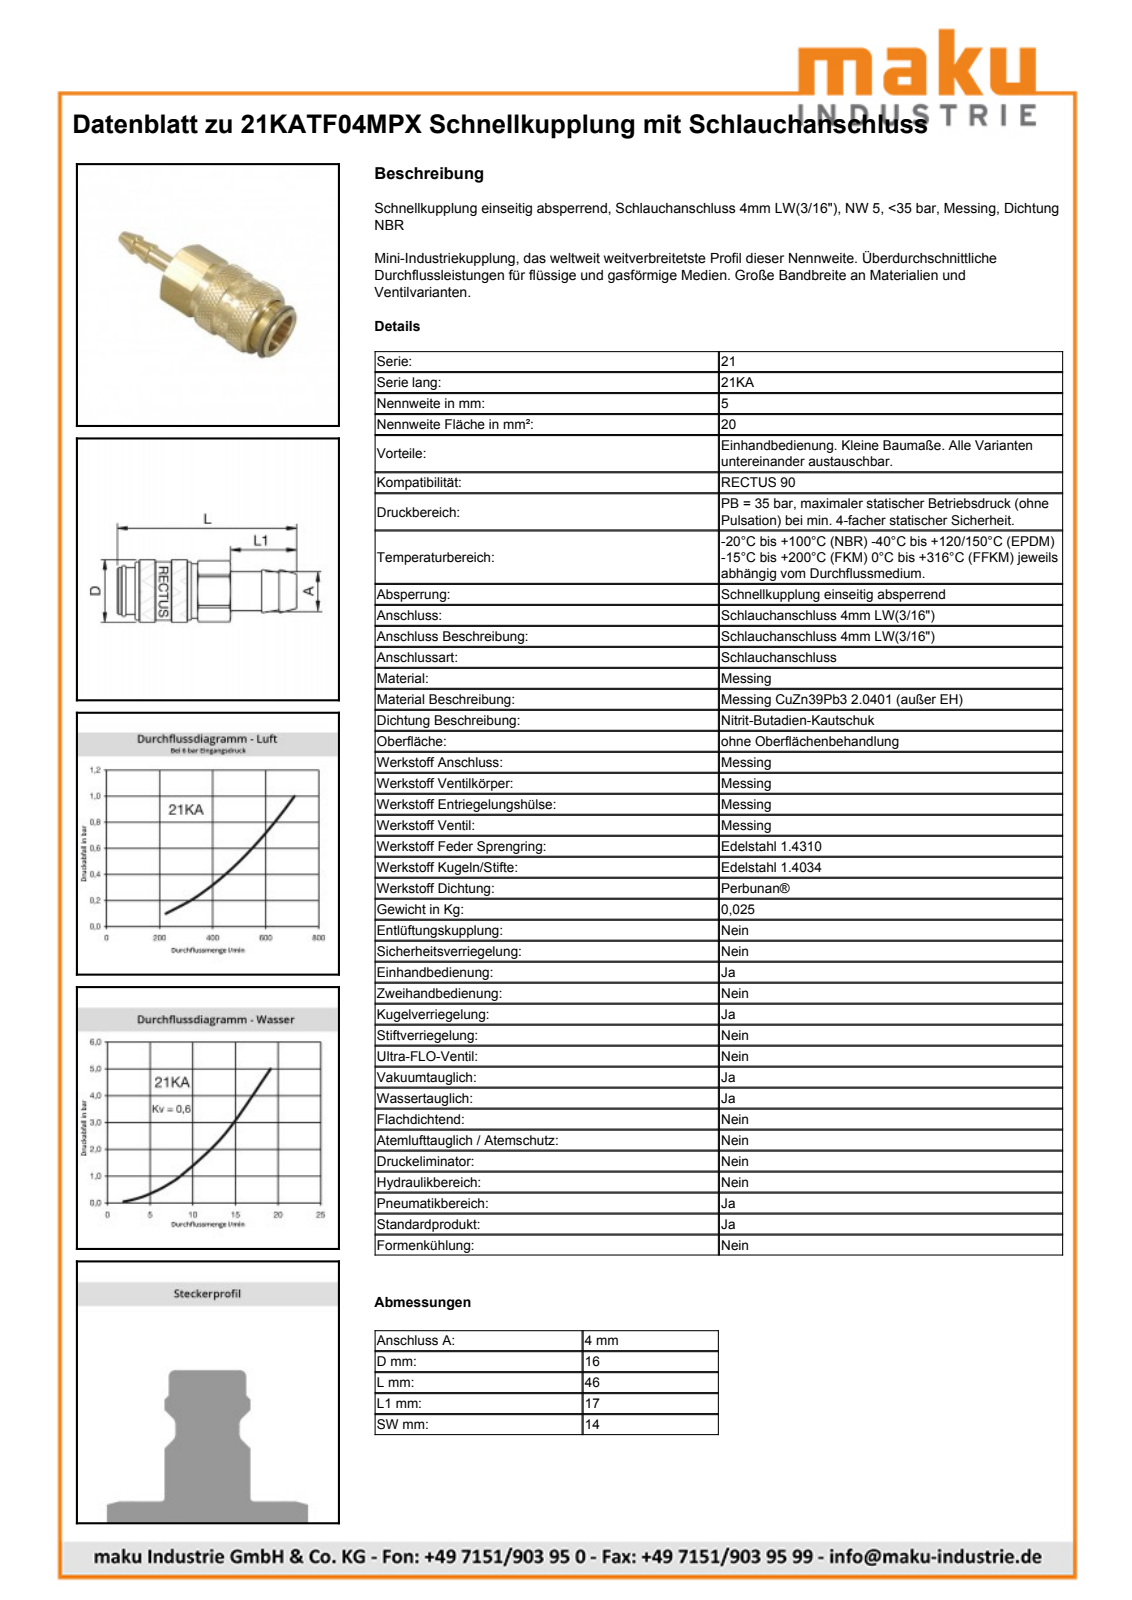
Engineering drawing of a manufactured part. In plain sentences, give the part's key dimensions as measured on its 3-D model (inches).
The part is named "D106502". Its 3-D file was written by "Autodesk Inventor 2011 (AUTOMOTIVE_DESIGN)". It is 2 solids with 402 faces: 132 planar, 61 cylindrical and 209 other. Overall it measures 1.817 by 0.636 by 0.636 inches. Its volume is 0.3 cubic inches and its surface area 5.292 square inches. Round holes: 1 of diameter 0.478, 1 of diameter 0.551. Round bosses or shafts: 1 of diameter 0.636, 1 of diameter 0.594, 1 of diameter 0.472, 1 of diameter 0.449, 1 of diameter 0.439, 1 of diameter 0.423, 1 of diameter 0.159. Partial cylindrical surfaces (rounded edges, fillets, slot ends): 1 of radius 0.293, 1 of radius 0.311. The main face-to-face distances are 0.551, 1.148, 0.455, 0.636, 0.512, 0.181, 0.967, 0.469, 0.287, 0.167.
